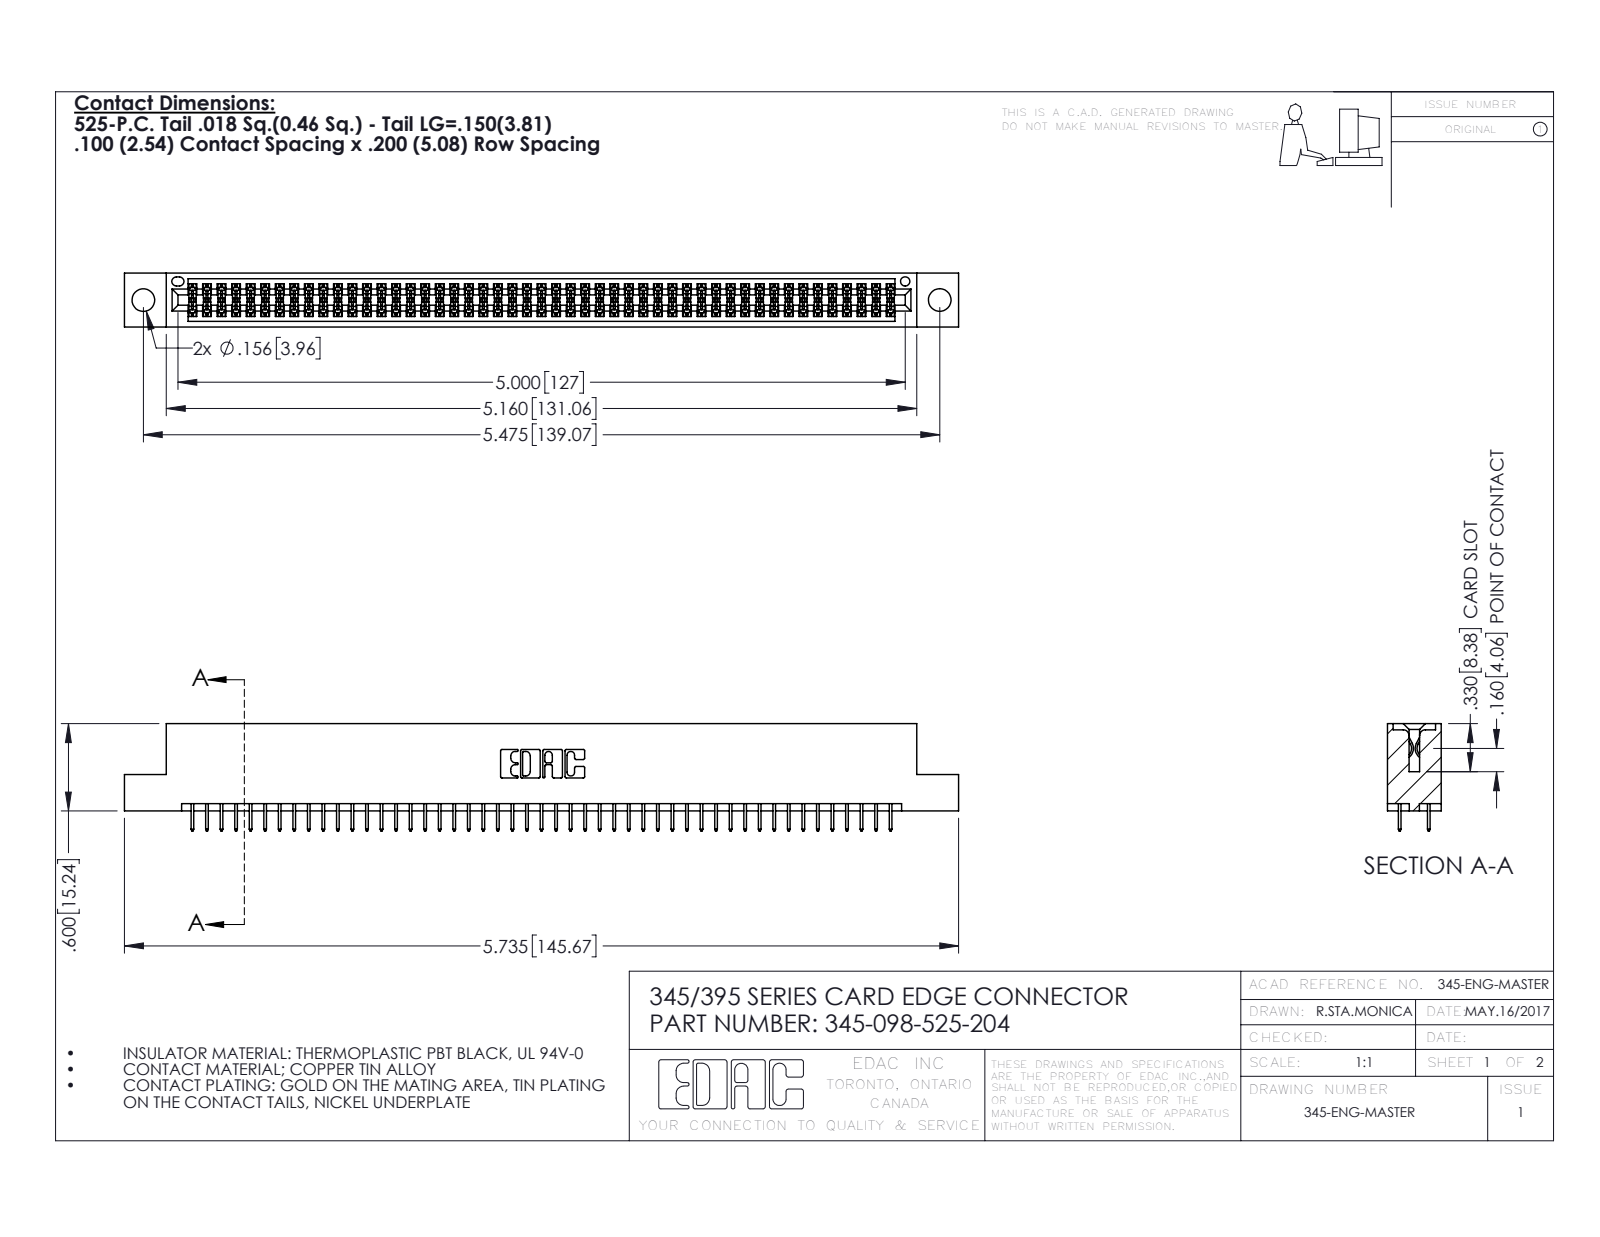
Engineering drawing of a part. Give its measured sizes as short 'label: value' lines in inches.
name: 345 Part_Flush Mounting Lugs - 0.156 Dia-TH; 345-292-001_345-293-125; 345-098-525-204
written by: SolidWorks 2020 (CONFIG_CONTROL_DESIGN)
unit: in
bodies: 99 solids, 5418 faces (3902 planar, 1516 cylindrical, 0 other)
size: 5.735 × 0.737 × 0.37
volume: 0.852 in³; area: 31.17 in²
holes: 2× ⌀0.156, 1× ⌀0.064
rounds: 196× R0.006, 22× R0.01, 6× R0.007, 6× R0.031, 3× R0.026, 2× R0.014, 2× R0.019, 2× R0.022
face distances: 0.298, 0.072, 0.2, 0.37, 0.098, 0.272, 0.025, 0.225, 0.072, 0.175
hole spacings: 0.27, 5.239, 5.475
